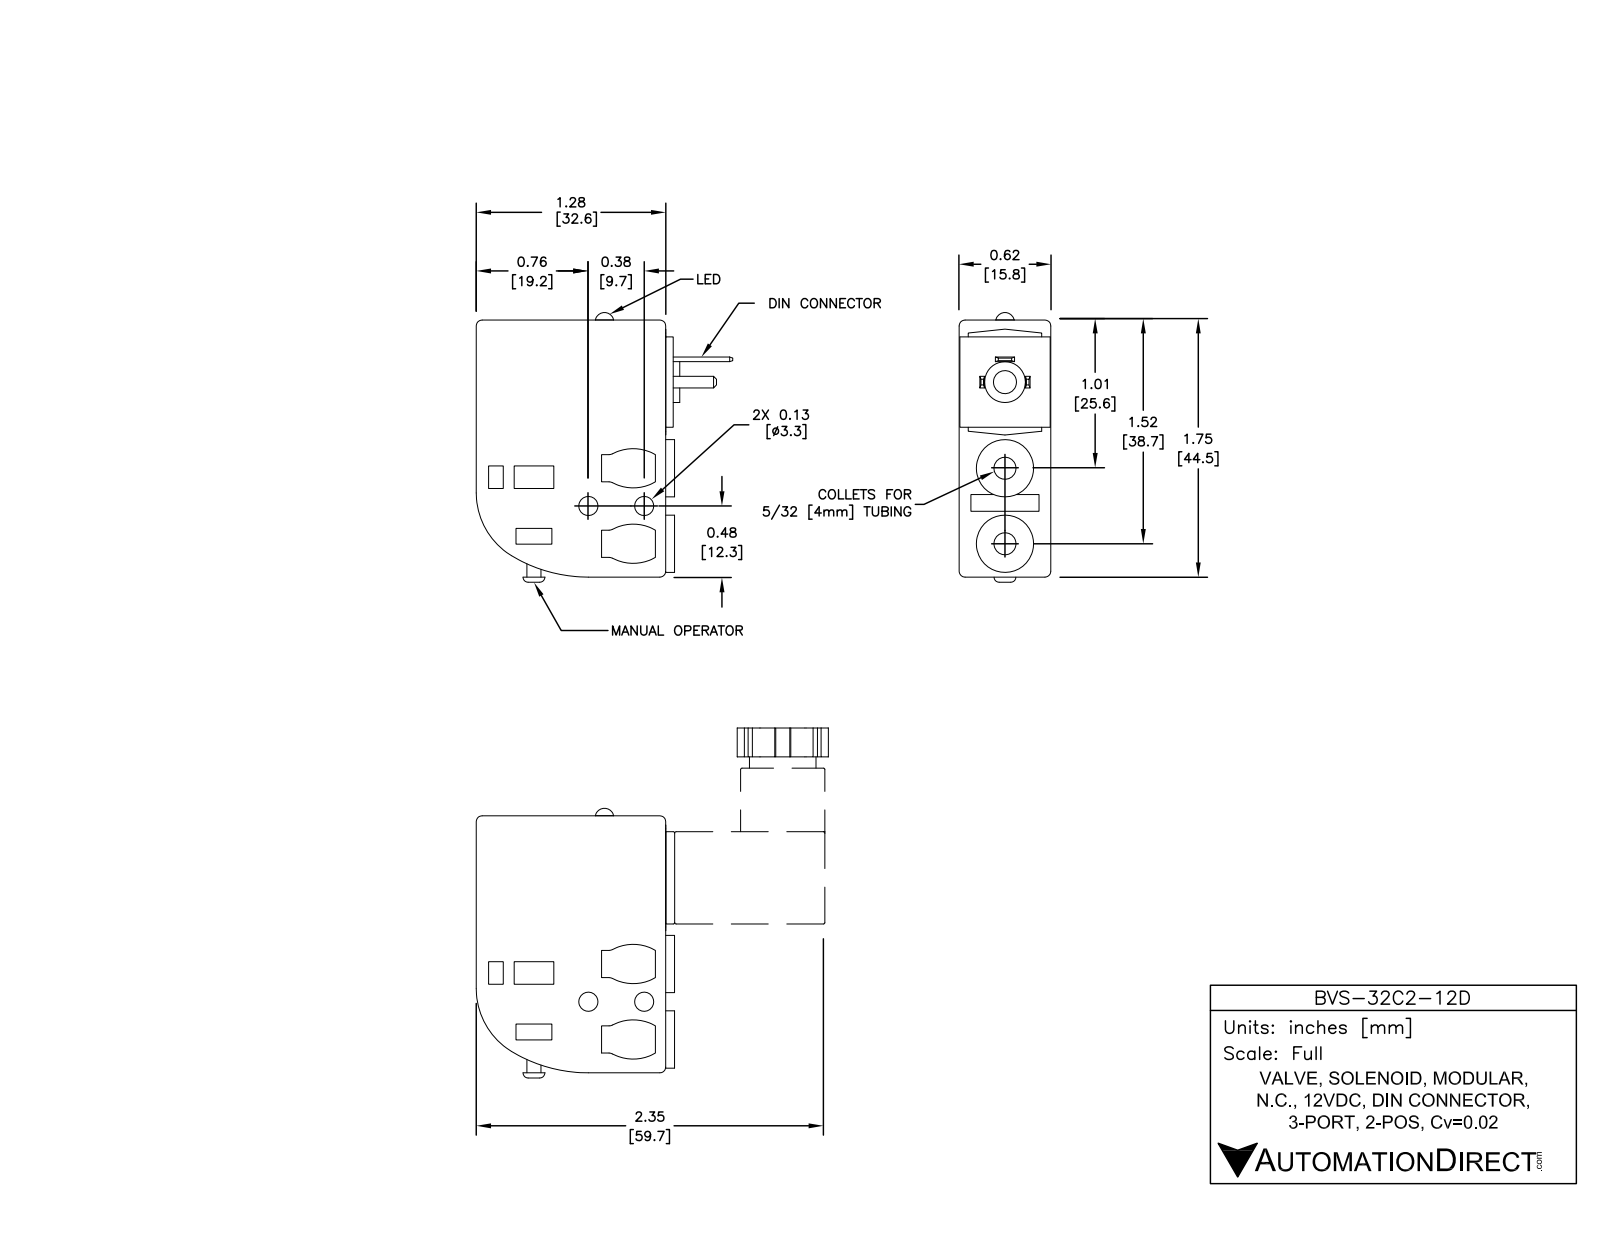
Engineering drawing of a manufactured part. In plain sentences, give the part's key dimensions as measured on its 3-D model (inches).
The part is named "BVS-32C2-12D". Its 3-D file was written by "SolidWorks 2013 (AUTOMOTIVE_DESIGN)". It is 2 solids with 204 faces: 135 planar, 56 cylindrical and 13 other. Overall it measures 1.836 by 1.743 by 0.624 inches. Its volume is 1.28 cubic inches and its surface area 11 square inches. Round holes: 2 of diameter 0.13, 2 of diameter 0.15, 2 of diameter 0.254, 1 of diameter 0.046, 1 of diameter 0.157. Round bosses or shafts: 2 of diameter 0.39, 1 of diameter 0.278, 1 of diameter 0.124, 1 of diameter 0.096. Partial cylindrical surfaces (rounded edges, fillets, slot ends): 11 of radius 0.04, 4 of radius 0.05, 4 of radius 0.3, 1 of radius 0.5, 1 of radius 1. The main face-to-face distances are 0.624, 0.1, 0.524, 1.287, 0.05, 0.051, 1.338, 1.75, 1.288, 0.424. The hole center spacings are 0.061, 0.38, 0.453, 0.514, 0.587, 0.648, 1.1.
